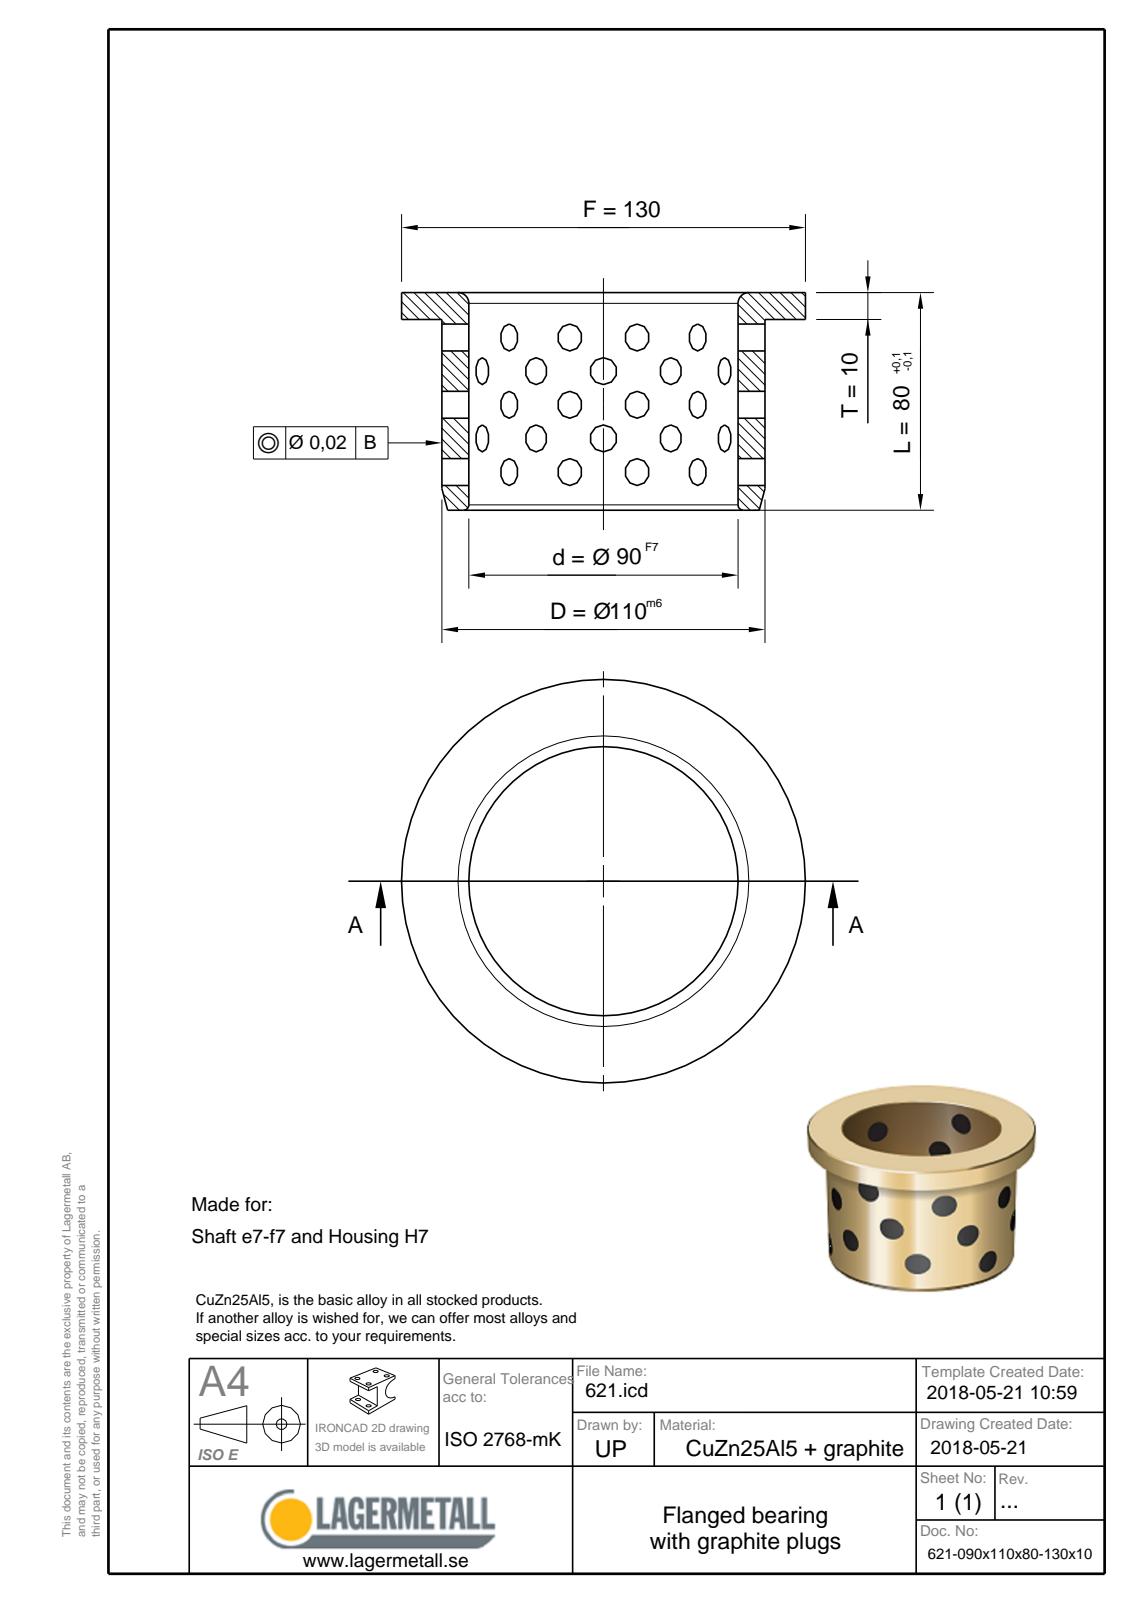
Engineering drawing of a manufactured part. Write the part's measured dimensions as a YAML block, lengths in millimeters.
part_name: "621-090x110x80-130x10"
step_written_by: "Spatial InterOp 3D (CONFIG_CONTROL_DESIGN)"
units: millimeters
bodies: {solids: 1, faces: 9, planar: 3, cylindrical: 3, other: 3}
overall_size: [130, 130, 80]
volume: 287492
surface_area: 63717
round_holes:
  - {diameter: 90, count: 1}
round_bosses_or_shafts:
  - {diameter: 130, count: 1}
  - {diameter: 110, count: 1}
face_to_face_distances: [10, 70, 80]
